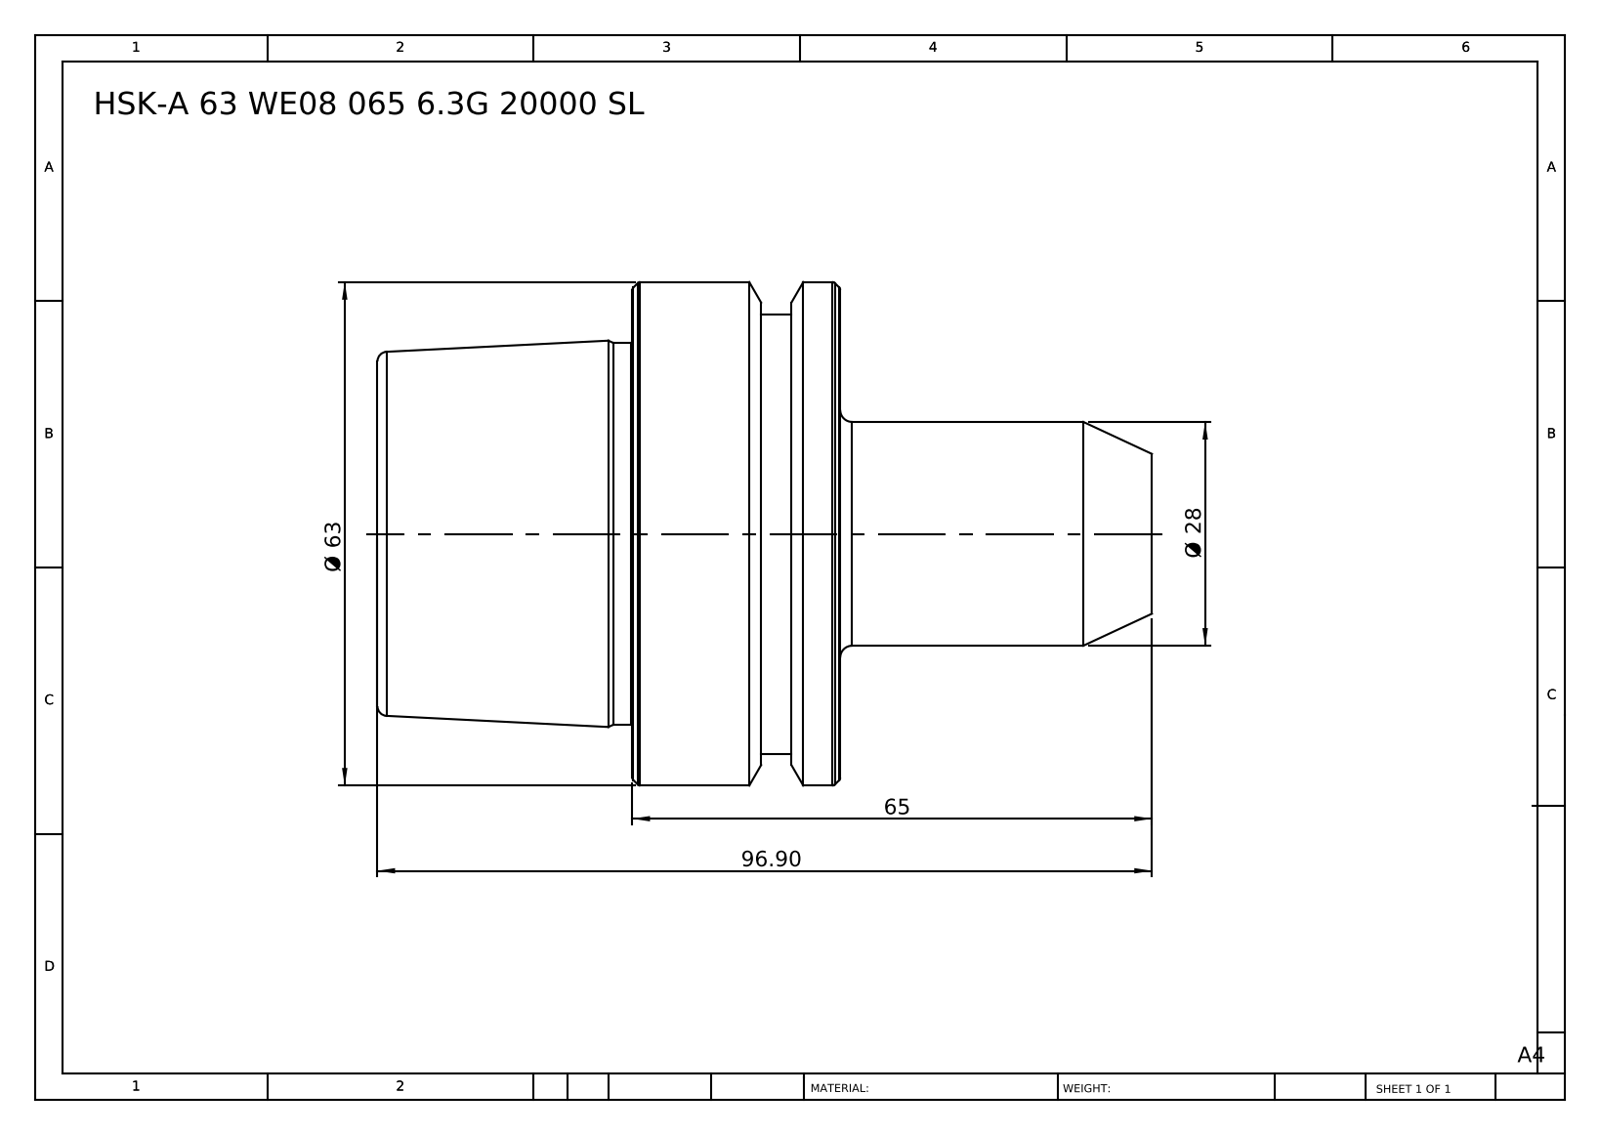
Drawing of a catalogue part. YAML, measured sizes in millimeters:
part_name: "HSK-A 63 WE08 065 6.3G 20000 SL"
step_written_by: "SolidWorks 2014 (CONFIG_CONTROL_DESIGN)"
units: millimeters
bodies: {solids: 1, faces: 46, planar: 6, cylindrical: 10, other: 30}
overall_size: [96.9, 63, 63]
volume: 155264
surface_area: 19680
round_bosses_or_shafts:
  - {diameter: 63, count: 1}
  - {diameter: 55, count: 1}
  - {diameter: 47.78, count: 1}
  - {diameter: 28, count: 1}
face_to_face_distances: [57.9, 26, 31.9, 39, 65, 96.9, 45.1, 6.1, 19.9, 51.8]
